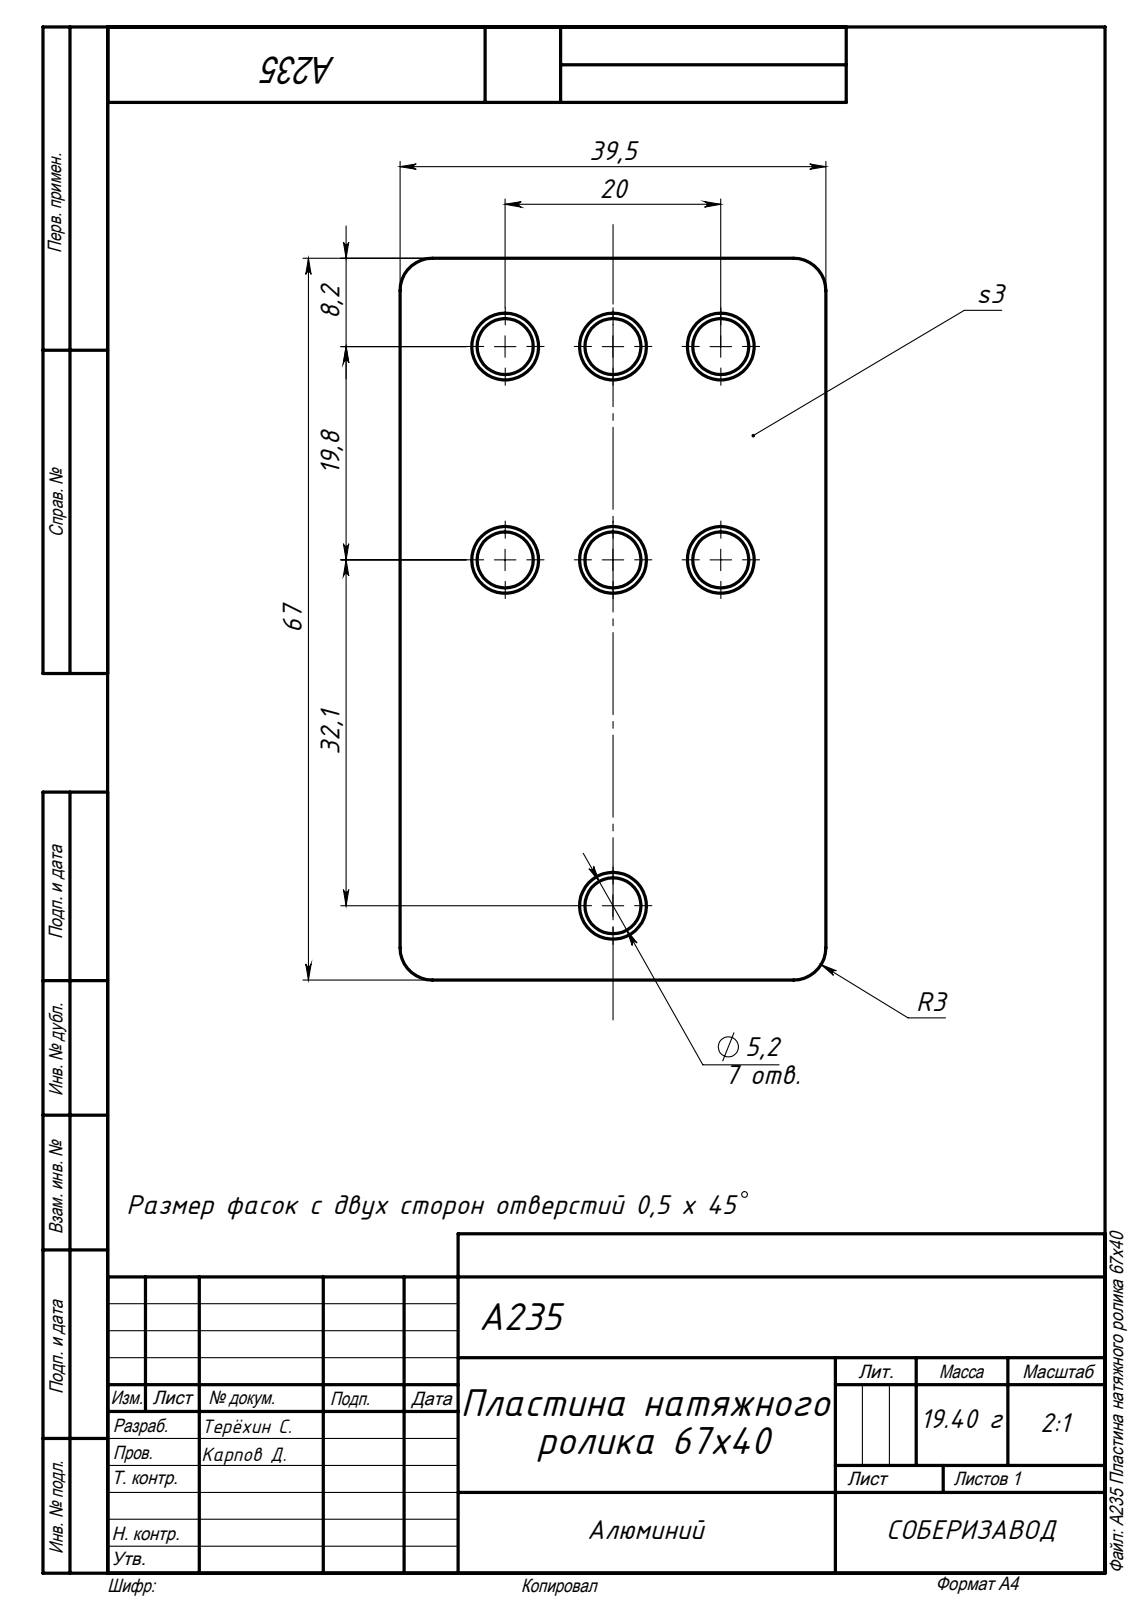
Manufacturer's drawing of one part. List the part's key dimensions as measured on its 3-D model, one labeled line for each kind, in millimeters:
Part name (STEP PRODUCT): A235 Пластина натяжного ролика 67x40
STEP written by: SolidWorks 2018 (AUTOMOTIVE_DESIGN)
Units: millimetres
Bodies: 1 solid, 52 faces (6 planar, 18 cylindrical, 28 other)
Overall size (bounding box): 67 × 39.5 × 3
Volume: 7 440 mm³ · Surface area: 5 884 mm²
Round holes (diameter × count): ⌀5.2 ×7
Partial cylindrical surfaces — rounded edges, fillets, slot ends (radius × count): R3 ×4
Main face-to-face distances: 3, 39.5, 67
Hole centre spacings: 10, 22.18, 19.8, 20, 28.14, 33.62, 52.85, 32.1
